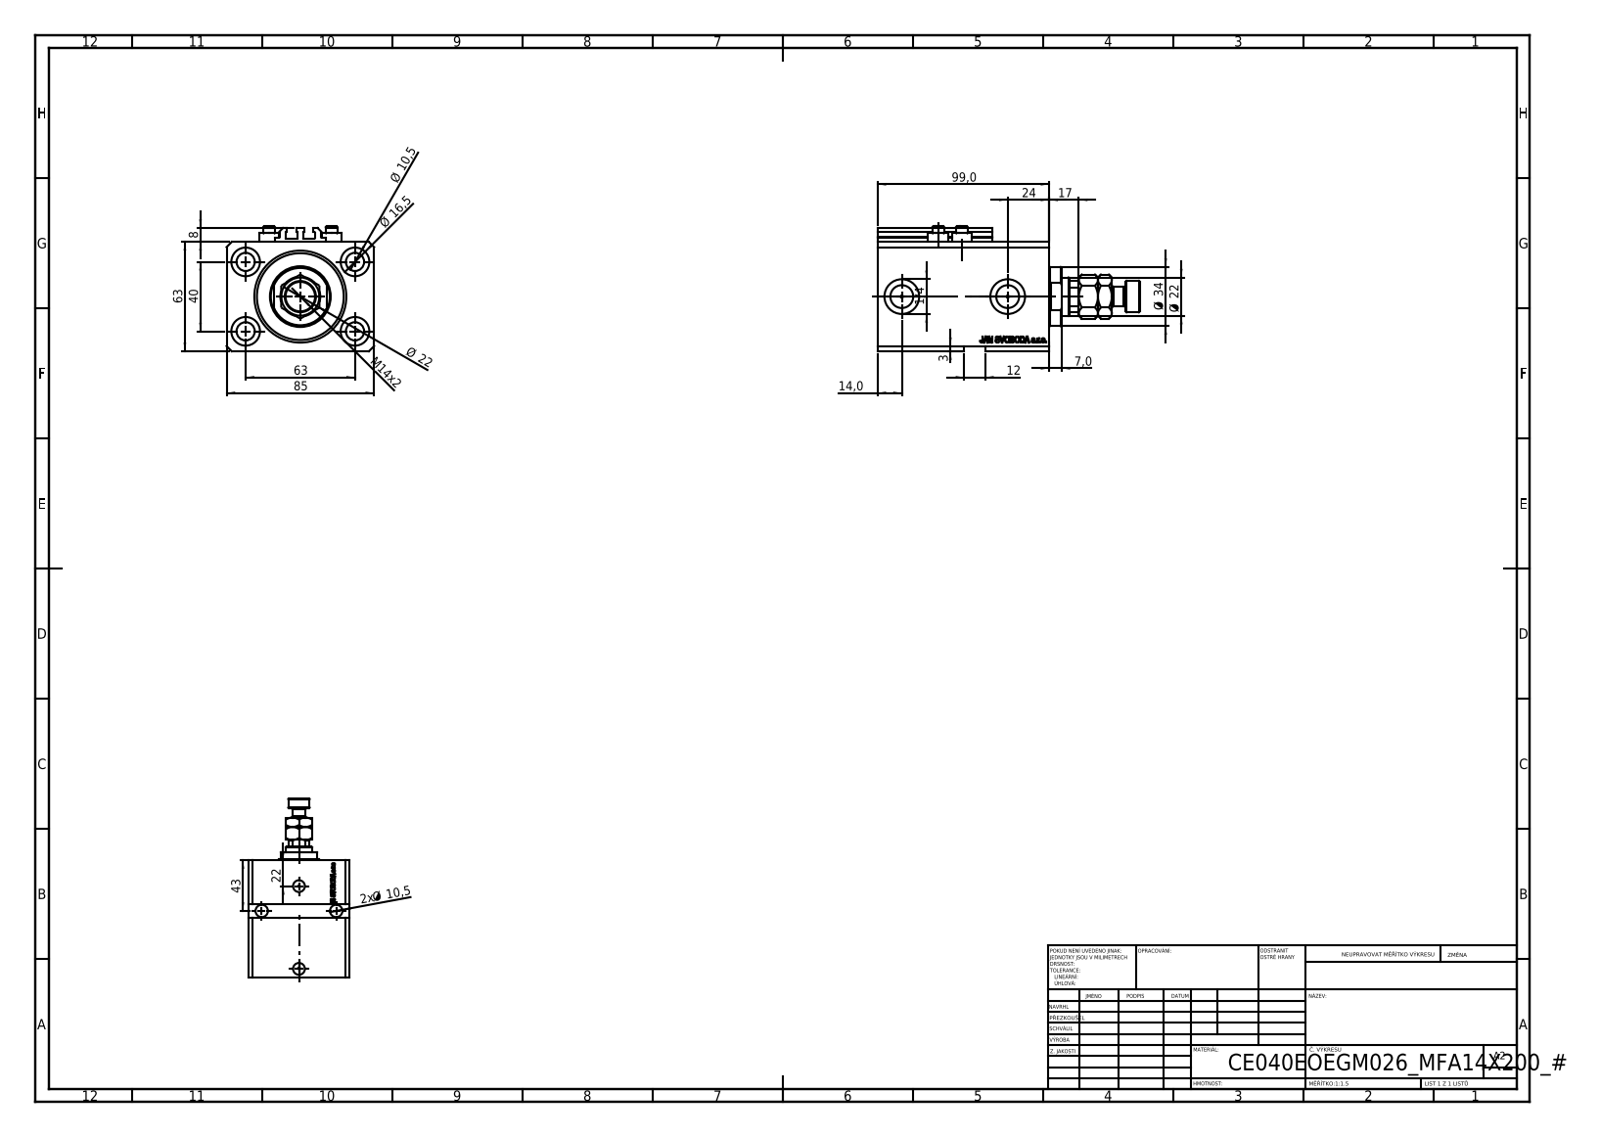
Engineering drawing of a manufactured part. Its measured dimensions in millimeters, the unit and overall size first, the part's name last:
Units: millimetres
Overall size (bounding box): 151 × 85 × 72
Round holes (diameter × count): ⌀10.5 ×6, ⌀1.25 ×4, ⌀4 ×4, ⌀16.5 ×4, ⌀10 ×2, ⌀13.16 ×2, ⌀20 ×2, ⌀12.5 ×1, ⌀22 ×1, ⌀40 ×1, ⌀53 ×1
Round bosses / shafts (diameter × count): ⌀11.6 ×4, ⌀7 ×4, ⌀34 ×1, ⌀18 ×1, ⌀11 ×1
Partial cylindrical surfaces — rounded edges, fillets, slot ends (radius × count): R0.2 ×10, R10.5 ×1
Main face-to-face distances: 63, 85, 17, 99, 82, 11.4, 70.6, 87.6, 3, 6
Hole centre spacings: 37.31, 63, 13.6, 15.4, 24.96, 32.84, 33.29, 33.62
Volume: 473 383 mm³ · Surface area: 103 316 mm²
Bodies: 9 solids, 1139 faces (551 planar, 130 cylindrical, 458 other)
Part name (STEP PRODUCT): V250CE_E_Body; ALLEN BOLT V250CE; V250CE_C_VCP; MFA (+1 more)
STEP written by: SolidWorks 2019 (CONFIG_CONTROL_DESIGN)
